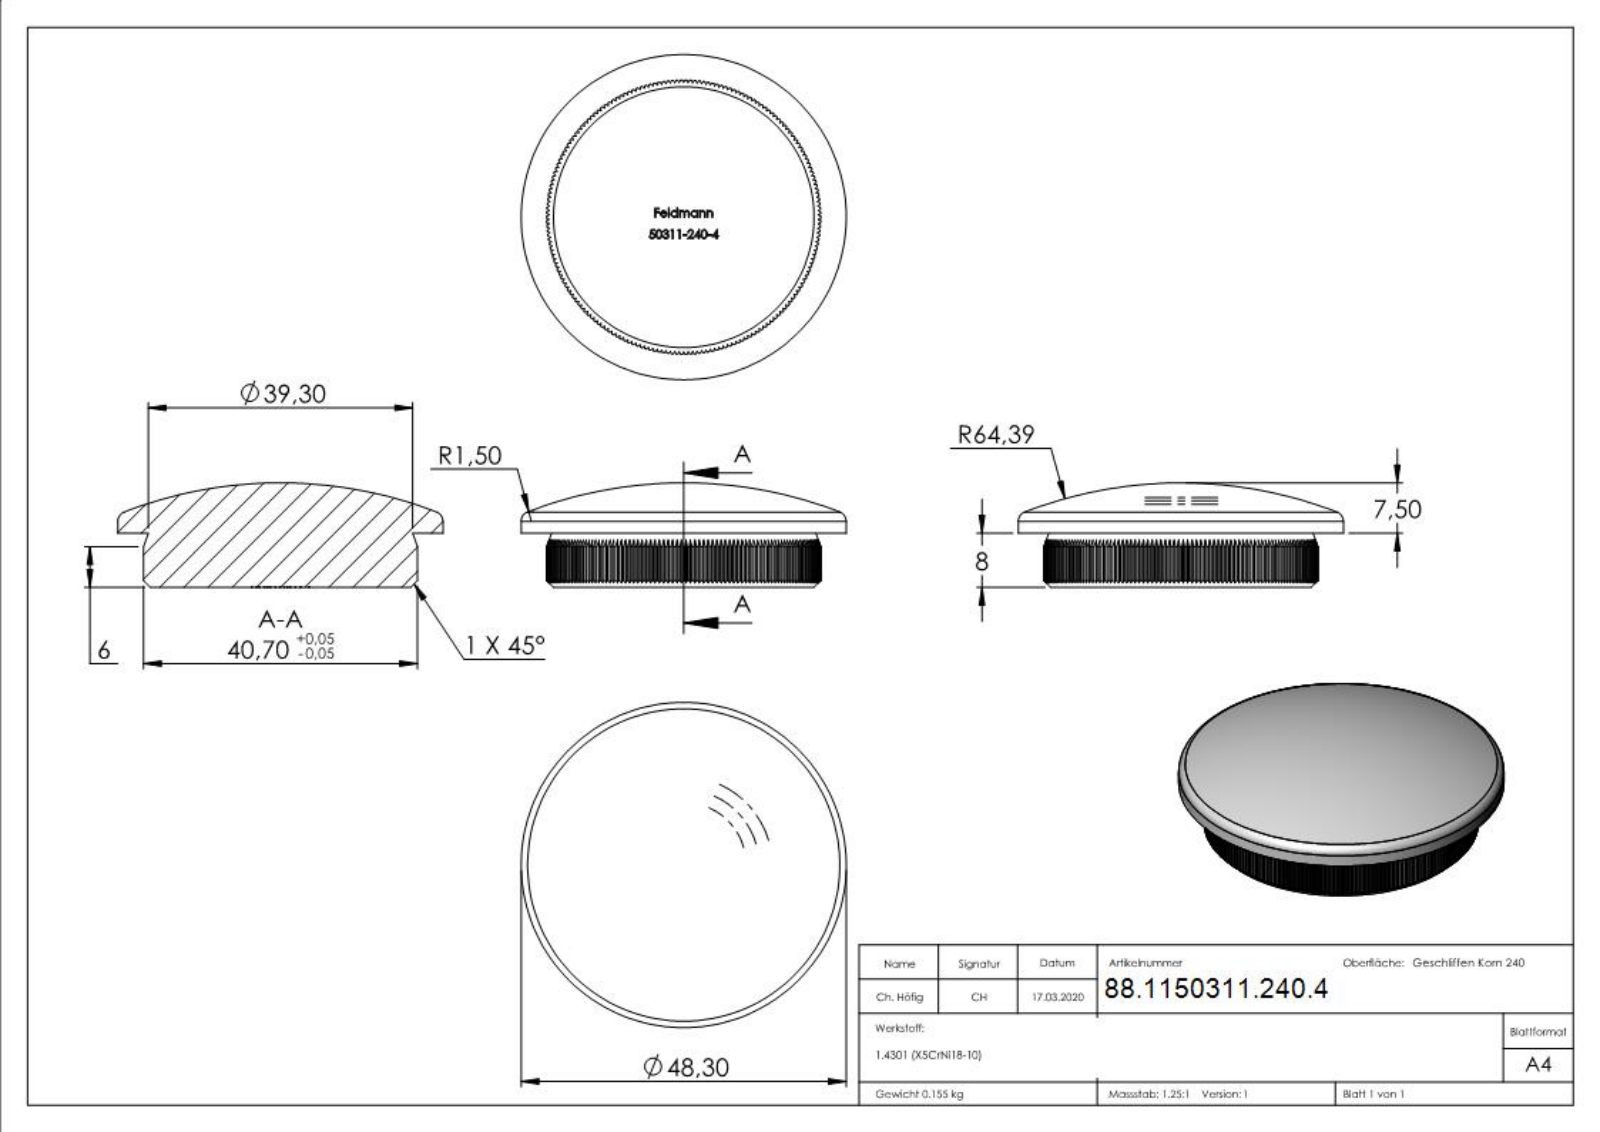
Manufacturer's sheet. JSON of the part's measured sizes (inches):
{"part_name": "50311-240-4", "step_written_by": "SolidWorks 2015 (CONFIG_CONTROL_DESIGN)", "units": "inches", "bodies": {"solids": 1, "faces": 812, "planar": 523, "cylindrical": 191, "other": 98}, "overall_size": [1.902, 1.902, 0.61], "volume_in3": 1.199, "surface_area_in2": 8.683, "round_bosses_or_shafts": [[1.902, 1]], "partial_cylinders_radius": [[0.801, 1]], "face_to_face_distances": [0.315, 0.787, 0.787, 0.788, 0.311, 0.04, 0.023, 0.126, 0.126, 0.014]}
